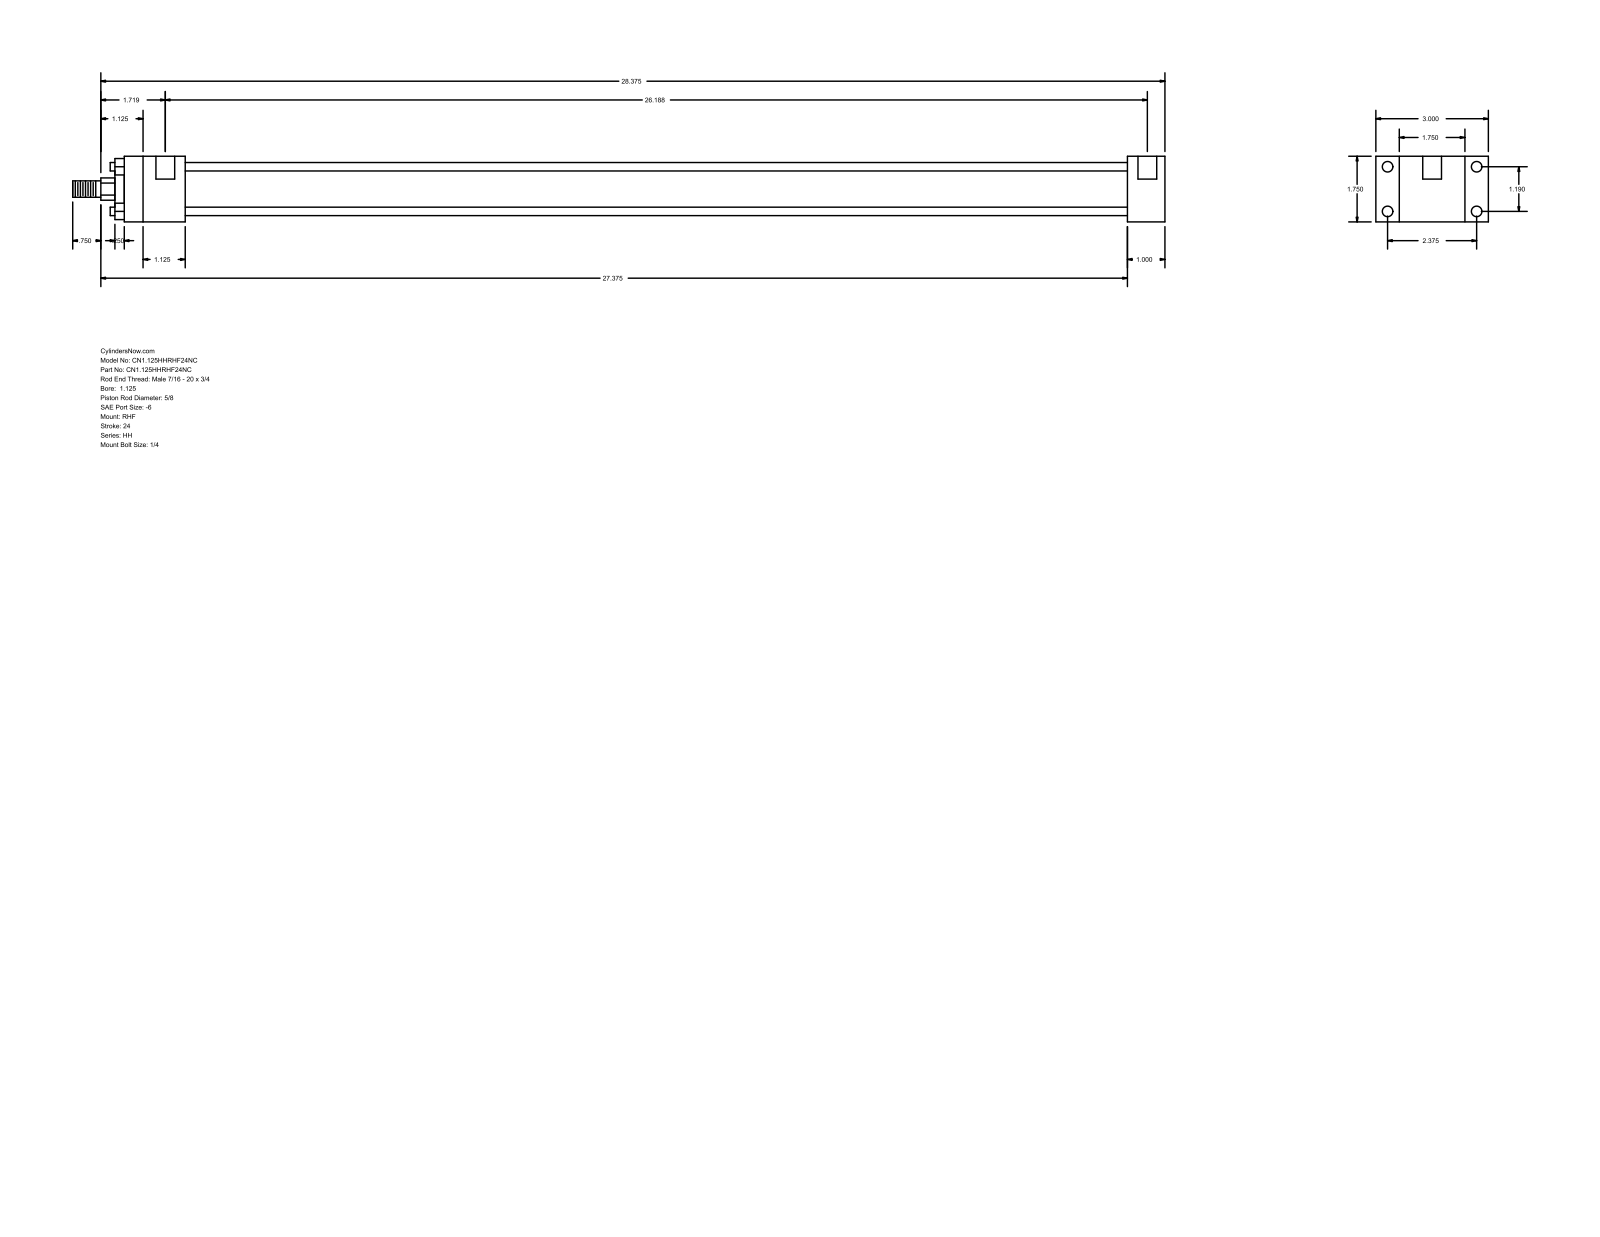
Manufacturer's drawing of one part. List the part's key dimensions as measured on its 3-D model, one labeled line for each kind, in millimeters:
Part name (STEP PRODUCT): HH_RHF__0112_0.625
STEP written by: GSSL Pune (CONFIG_CONTROL_DESIGN)
Units: millimetres
Bodies: 0 solids, 88 faces (60 planar, 28 cylindrical, 0 other)
Overall size (bounding box): 739.77 × 76.2 × 44.45
Round holes (diameter × count): ⌀5.56 ×4, ⌀7.14 ×4, ⌀12.7 ×2
Round bosses / shafts (diameter × count): ⌀5.71 ×4, ⌀34.92 ×1, ⌀28.57 ×1, ⌀15.88 ×1, ⌀11.11 ×1
Partial cylindrical surfaces — rounded edges, fillets, slot ends (radius × count): R7.54 ×1
Main face-to-face distances: 44.46, 15.87, 25.4, 60.33, 76.2, 638.18, 663.58, 41.27, 679.45, 704.85
Hole centre spacings: 30.22, 60.32, 67.47, 661.99, 3.17, 665.16
